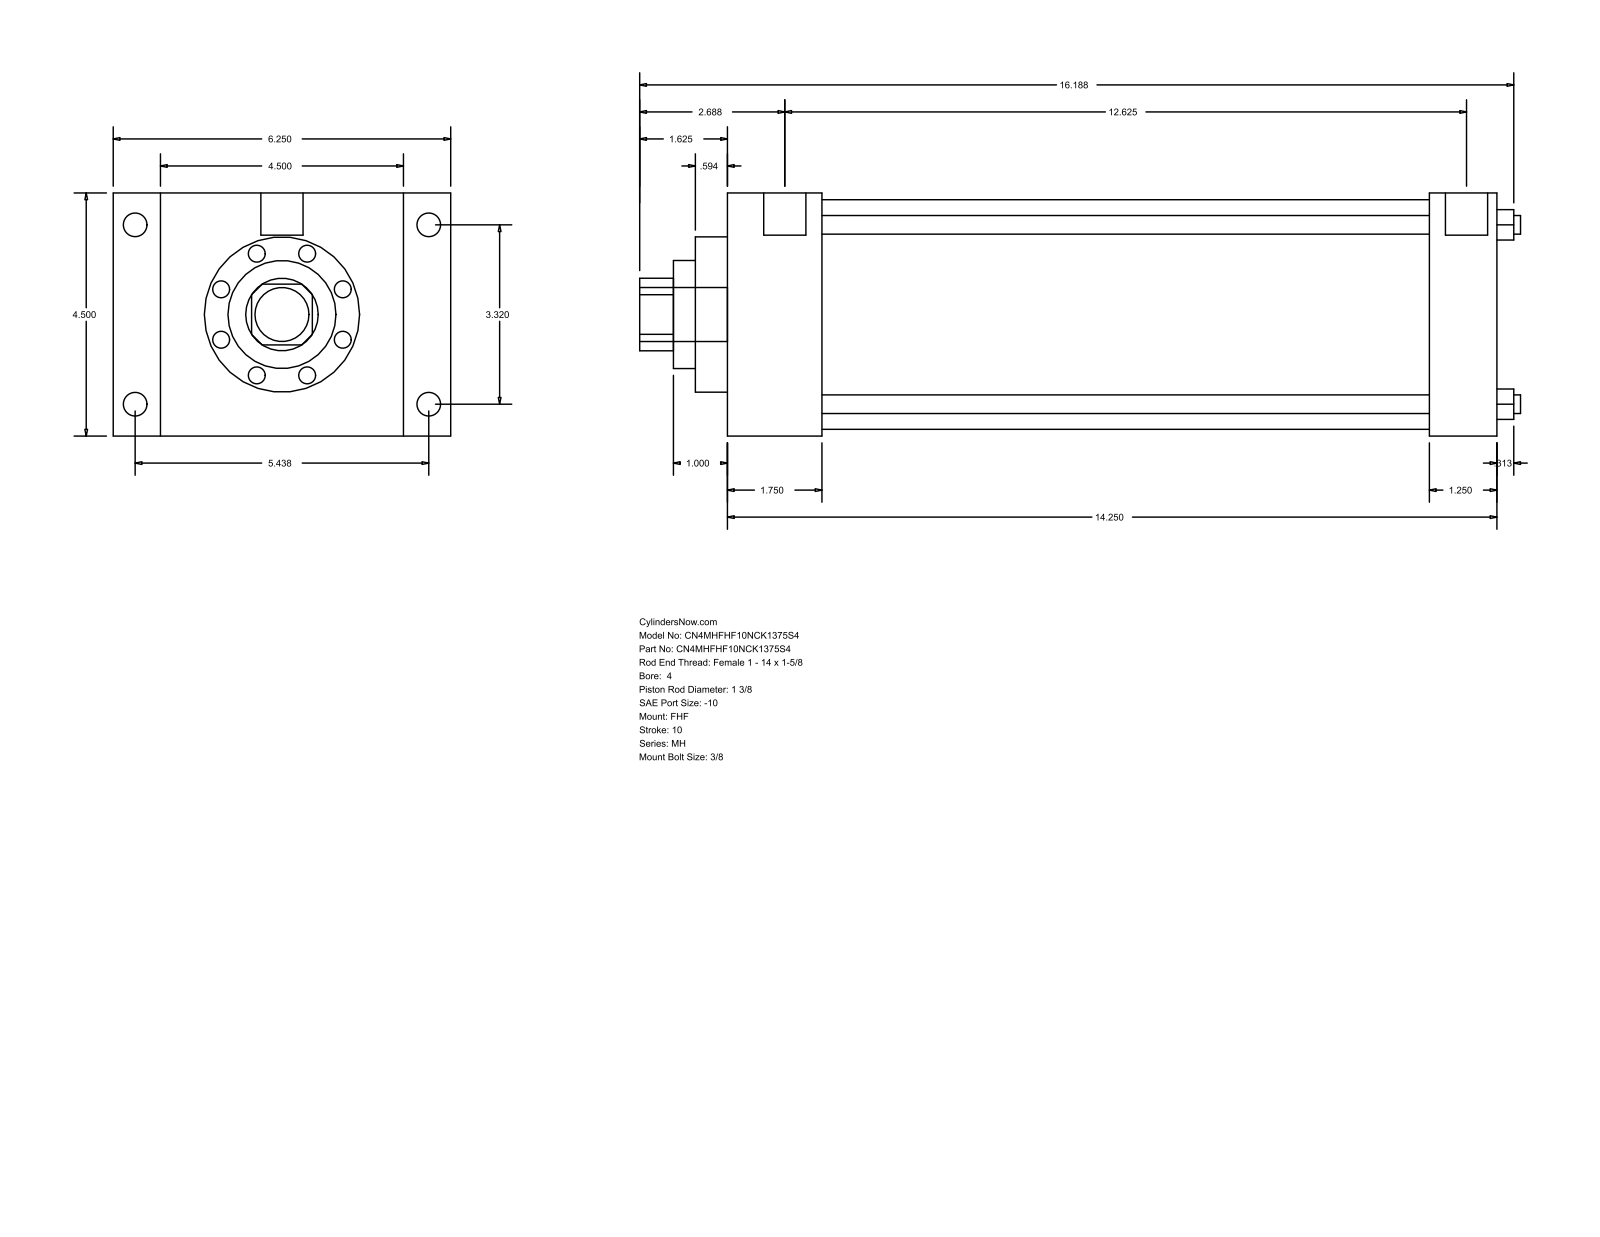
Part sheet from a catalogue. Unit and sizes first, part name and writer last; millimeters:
Units: millimetres
Overall size (bounding box): 414.34 × 158.75 × 114.3
Round holes (diameter × count): ⌀8.76 ×4, ⌀34.92 ×1, ⌀50.8 ×1, ⌀73.03 ×1, ⌀107.95 ×1
Round bosses / shafts (diameter × count): ⌀11.13 ×4, ⌀8.73 ×4, ⌀19.84 ×2, ⌀25.4 ×1
Partial cylindrical surfaces — rounded edges, fillets, slot ends (radius × count): R17.06 ×1
Main face-to-face distances: 114.3, 361.96, 44.45, 317.51, 22.23, 136.53, 158.76, 330.21, 285.76, 31.75
Hole centre spacings: 59.62, 84.32, 119.25
Bodies: 0 solids, 90 faces (61 planar, 29 cylindrical, 0 other)
Part name (STEP PRODUCT): MH_FHF__0400_1.375
STEP written by: GSSL Pune (CONFIG_CONTROL_DESIGN)
